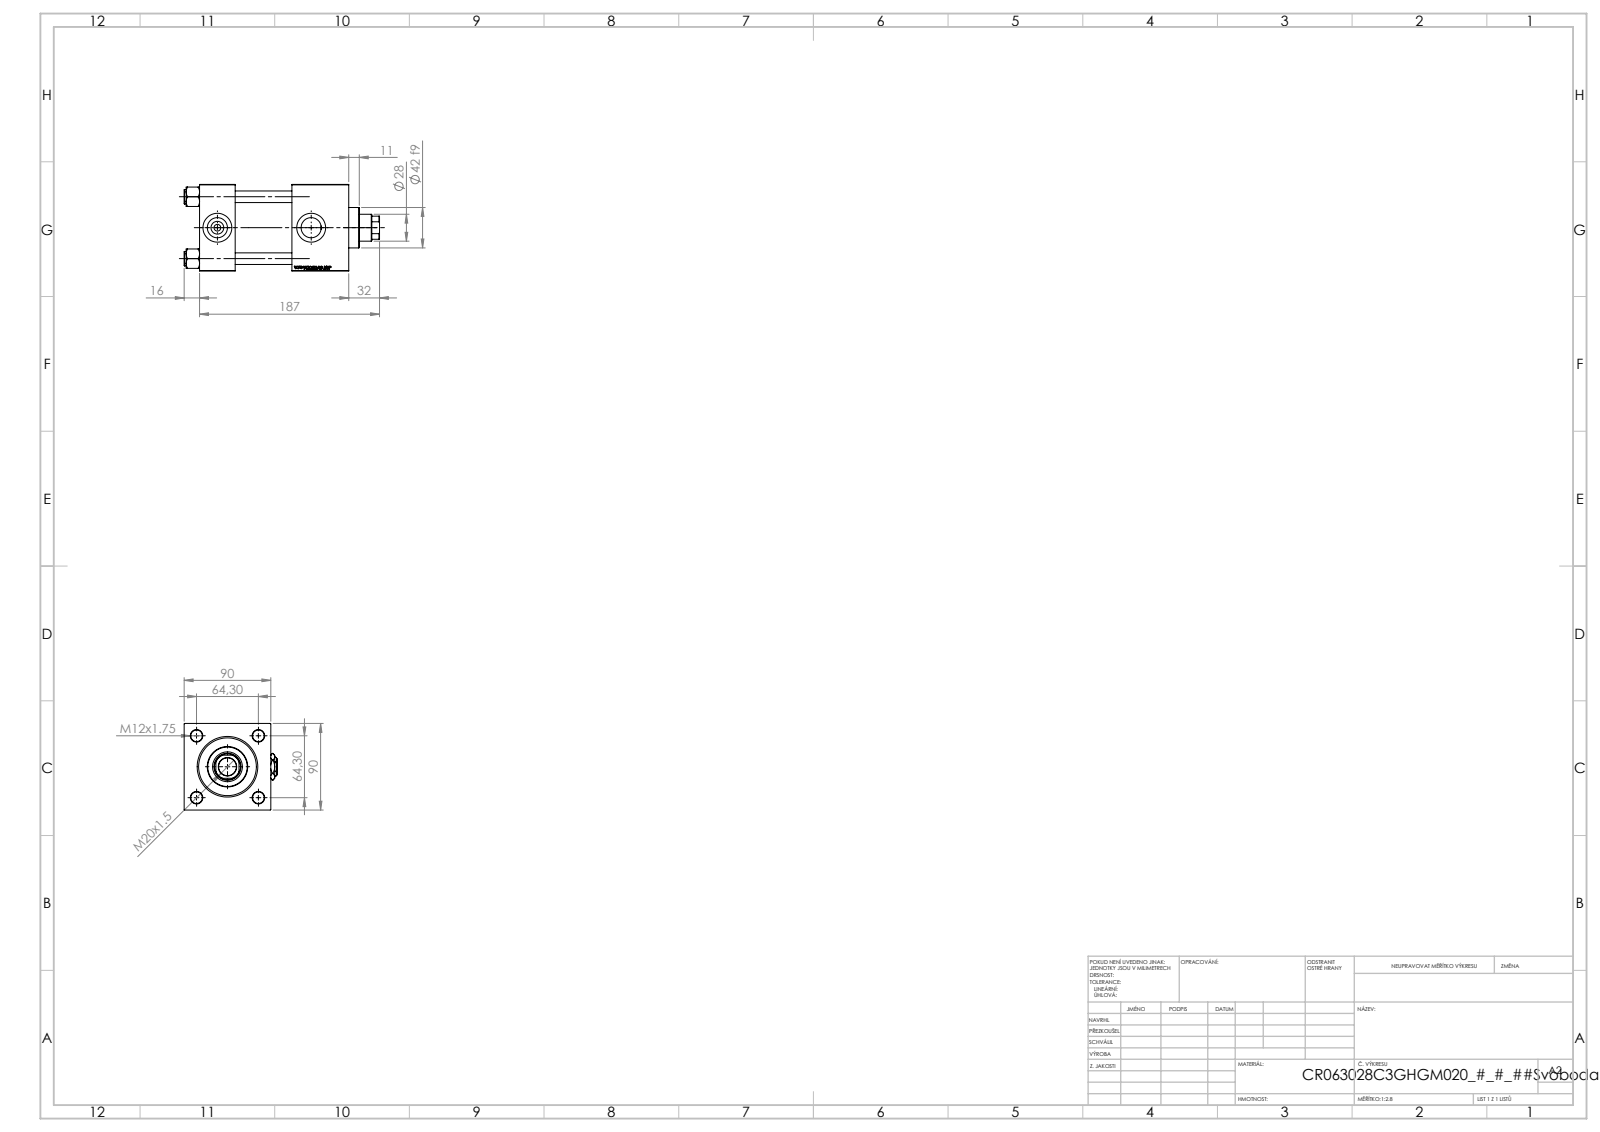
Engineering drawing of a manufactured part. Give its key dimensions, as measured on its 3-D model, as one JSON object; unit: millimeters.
{"part_name": "V215CR_C_Body; Zatka_pro_OIL_PORT; NUT_M5_C; V215_VC_A (+2 more)", "step_written_by": "SolidWorks 2019 (CONFIG_CONTROL_DESIGN)", "units": "millimeters", "bodies": {"solids": 13, "faces": 1250, "planar": 574, "cylindrical": 98, "other": 578}, "overall_size": [203, 97, 90], "volume_mm3": 940483, "surface_area_mm2": 183915, "round_holes": [[12, 4], [7, 2], [20.96, 2], [30, 2], [18.5, 1], [28, 1], [31, 1], [50, 1], [60, 1], [63, 1]], "round_bosses_or_shafts": [[15, 4], [69, 1], [42, 1]], "partial_cylinders_radius": [[13.5, 1]], "face_to_face_distances": [90, 59, 37, 118, 155, 96, 126.3, 89.3, 30.3, 28.7], "hole_center_spacings": [45.47, 64.3, 90.93, 97.5]}
